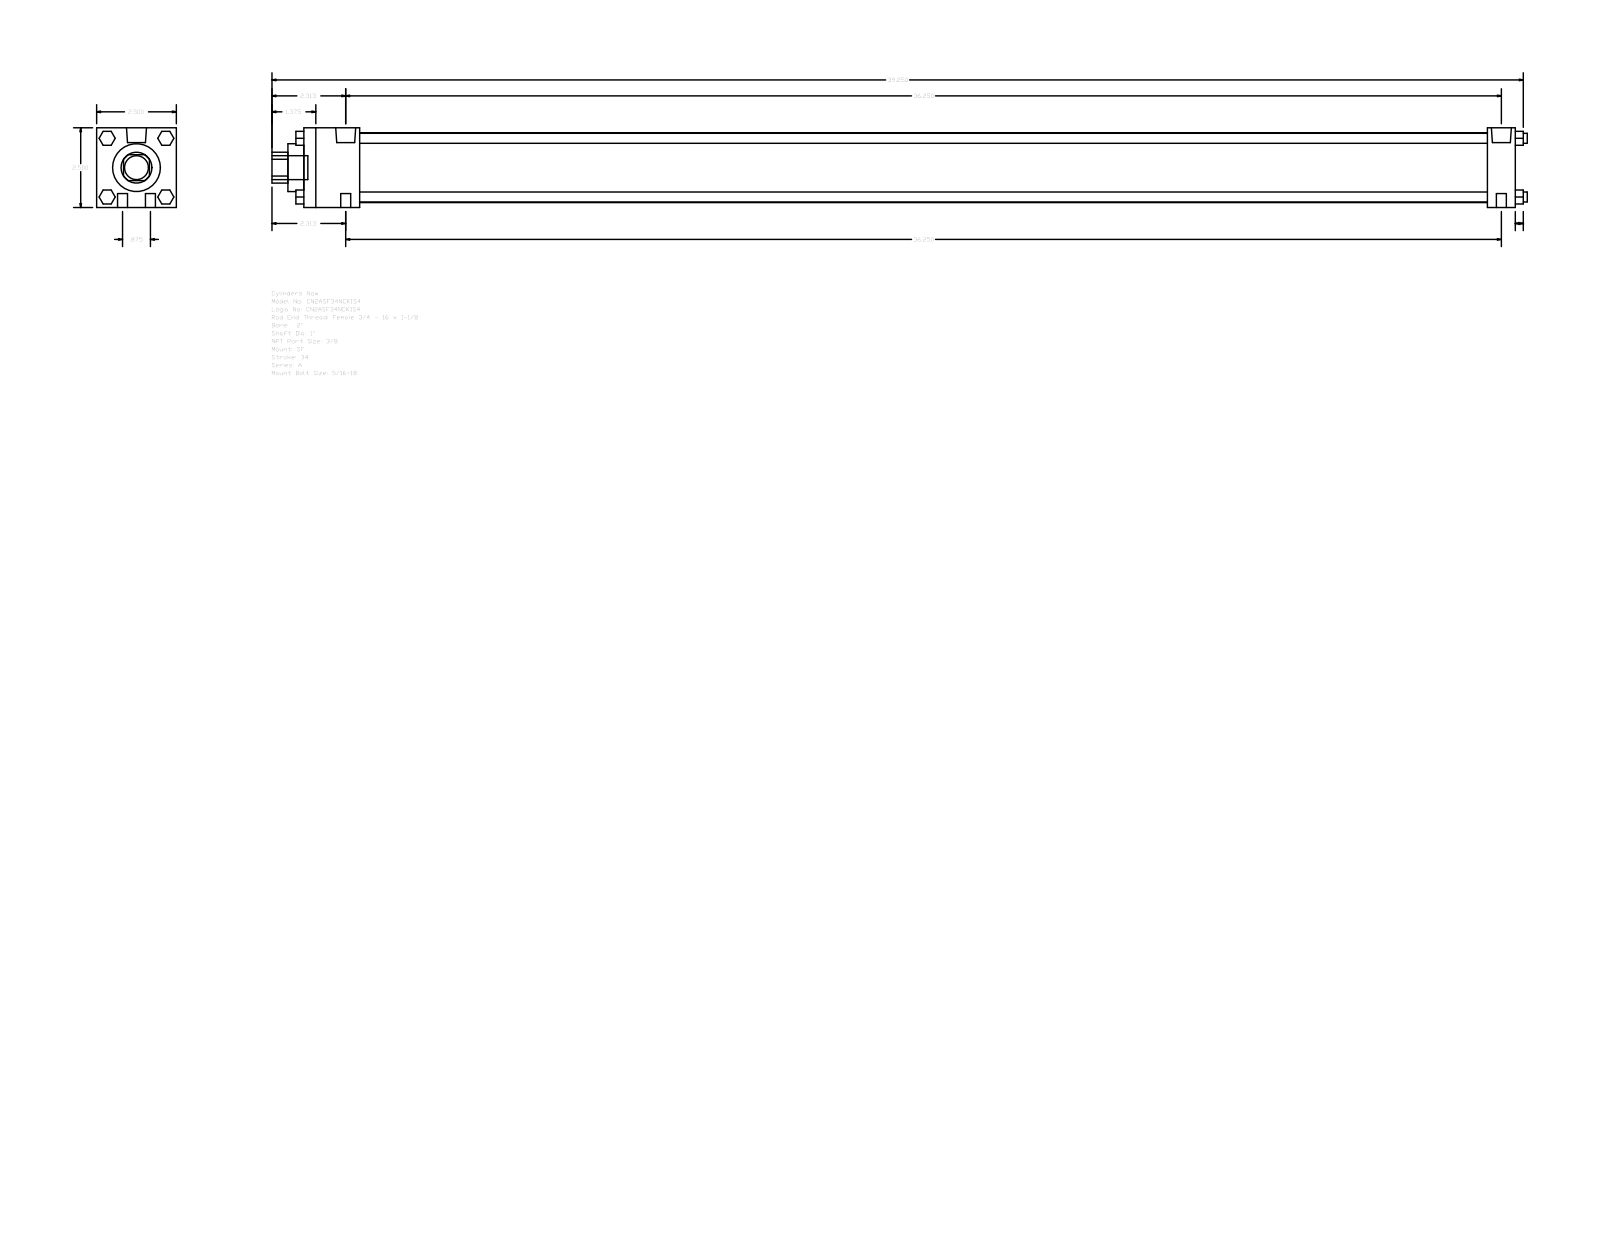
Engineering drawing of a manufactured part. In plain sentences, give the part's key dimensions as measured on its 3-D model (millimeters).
The part is named "A_SF__0200_1". Its 3-D file was written by "GSSL Pune (CONFIG_CONTROL_DESIGN)". It is 0 solids with 124 faces: 94 planar, 30 cylindrical and 0 other. Overall it measures 1000.12 by 63.5 by 63.5 millimeters. Round holes: 1 of diameter 25.4, 1 of diameter 38.1, 1 of diameter 55.63. Round bosses or shafts: 8 of diameter 7.94, 2 of diameter 15.93, 2 of diameter 5.56, 1 of diameter 19.05. Partial cylindrical surfaces (rounded edges, fillets, slot ends): 1 of radius 12.29. The main face-to-face distances are 63.5, 965.2, 942.98, 22.22, 44.45, 898.53, 920.75, 12.7, 977.9, 6.35.
